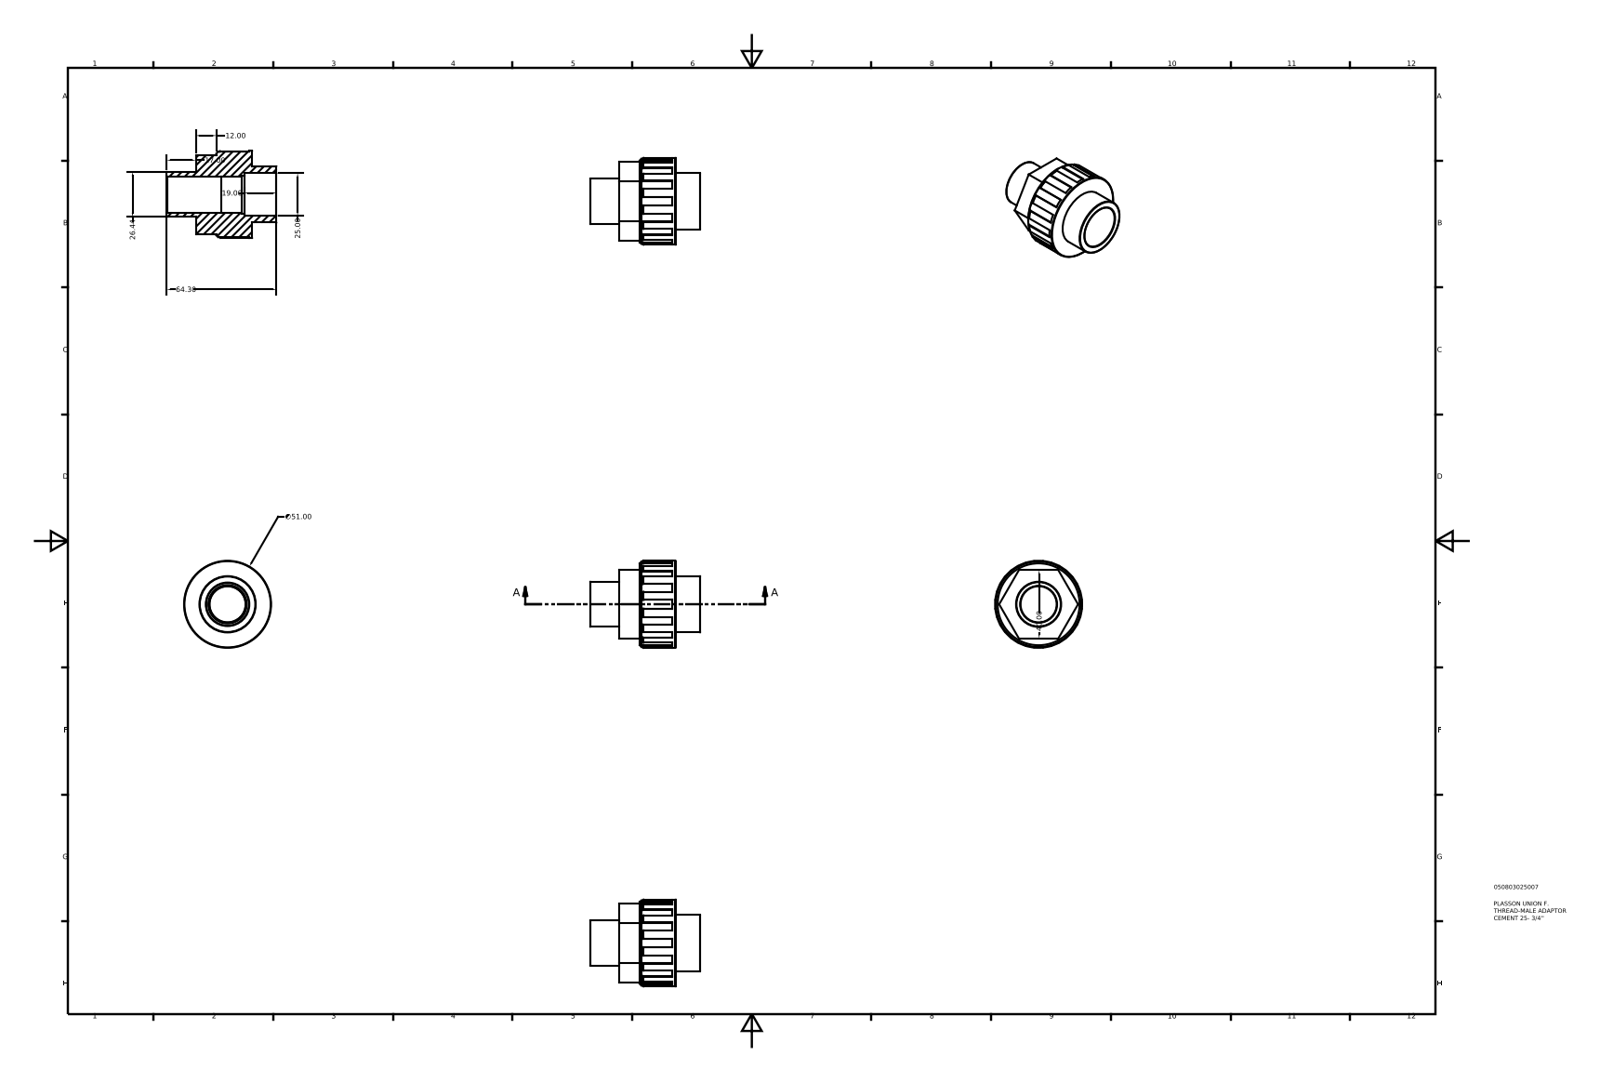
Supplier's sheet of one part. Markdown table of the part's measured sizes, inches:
| quantity | value |
| --- | --- |
| part name | 050803025007 |
| STEP written by | Autodesk Inventor 2015 (AUTOMOTIVE_DESIGN) |
| units | inches |
| bodies | 1 solid, 92 faces (62 planar, 8 cylindrical, 22 other) |
| overall size | 2.531 × 2.008 × 2.008 |
| volume | 3.347 in³ |
| surface area | 24.64 in² |
| round holes (diameter × count) | 0.833 × 1, 0.837 × 1, 0.886 × 1, 0.984 × 1 |
| round bosses / shafts (diameter × count) | 2.008 × 1, 1.968 × 1, 1.299 × 1, 1.041 × 1 |
| main face-to-face distances | 1.301, 1.575, 0.472, 0.829, 1.862, 1.39, 0.561, 0.669, 1.142, 1.97 |
